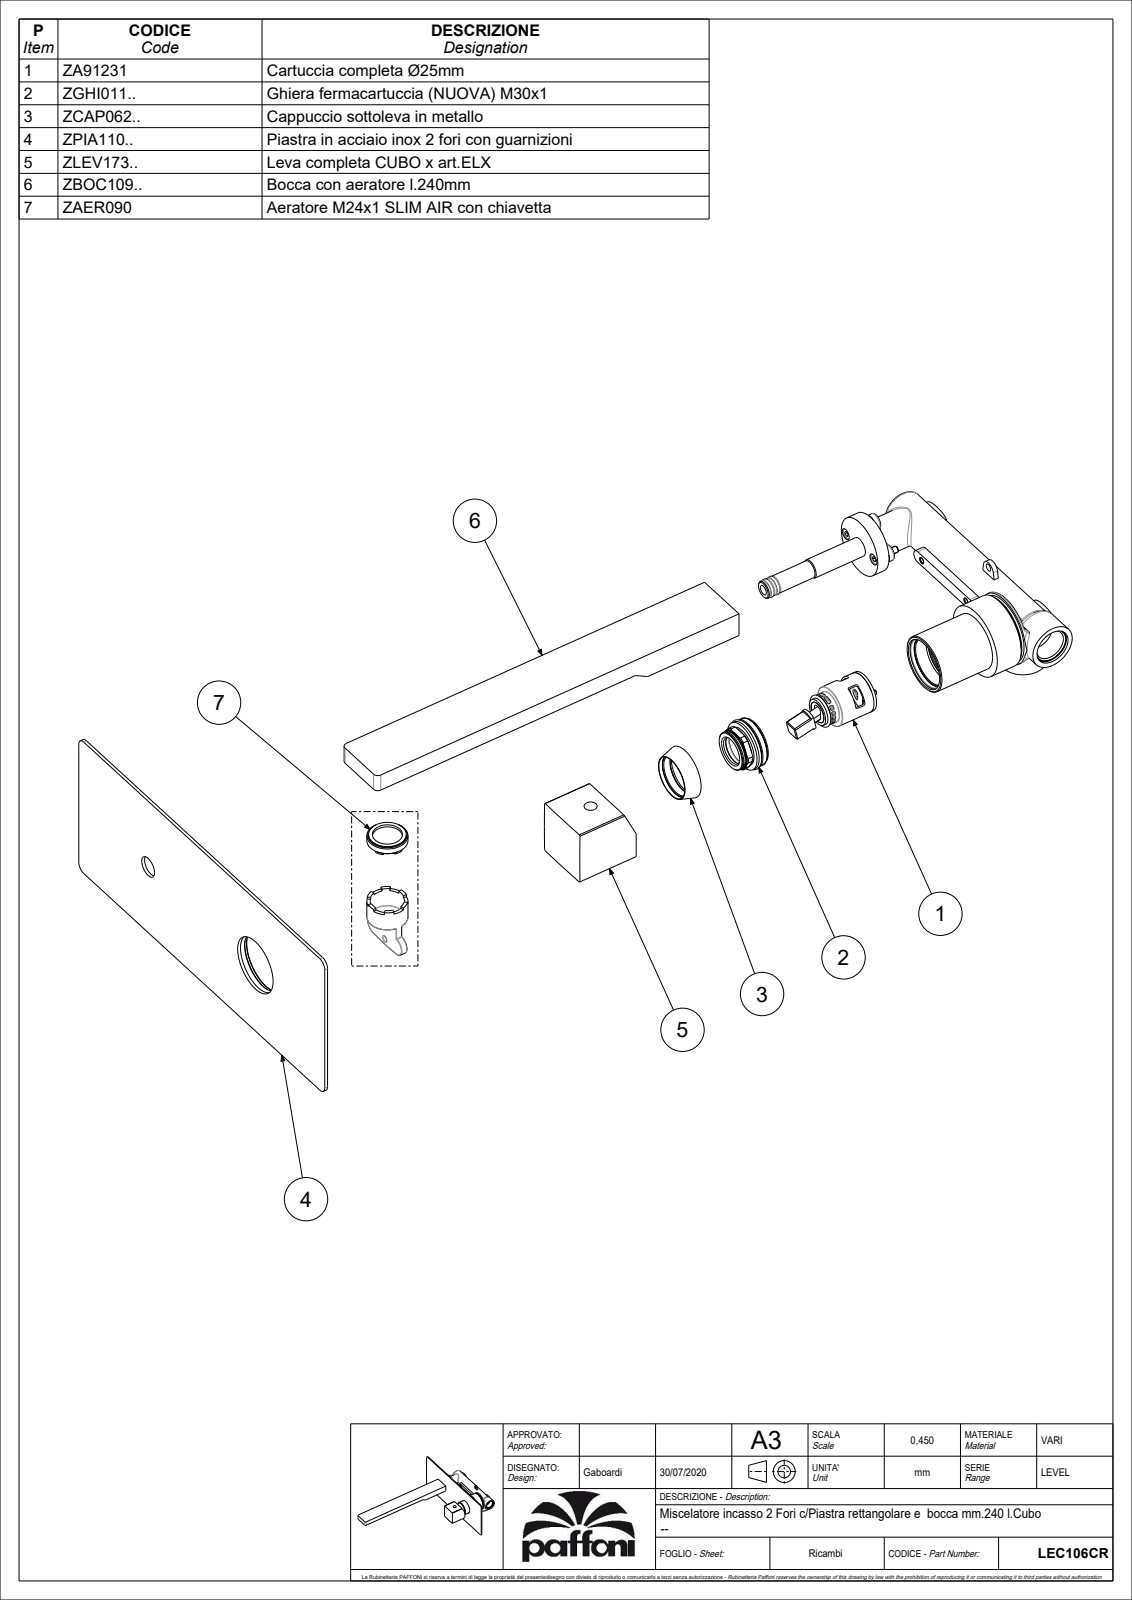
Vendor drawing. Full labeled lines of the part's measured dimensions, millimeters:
Part name (STEP PRODUCT): LEC106CR
STEP written by: CREO PARAMETRIC BY PTC INC, 2020044 (CONFIG_CONTROL_DESIGN)
Units: millimetres
Bodies: 2 solids, 713 faces (233 planar, 261 cylindrical, 219 other)
Overall size (bounding box): 260 × 250 × 100
Volume: 193 399 mm³ · Surface area: 110 237 mm²
Round holes (diameter × count): ⌀6 ×2, ⌀11 ×2, ⌀3 ×1, ⌀4.2 ×1, ⌀5.5 ×1, ⌀12 ×1, ⌀13 ×1, ⌀15 ×1, ⌀16.7 ×1, ⌀17 ×1, ⌀17.5 ×1, ⌀19.2 ×1
Round bosses / shafts (diameter × count): ⌀35.2 ×1, ⌀30 ×1, ⌀27.7 ×1, ⌀25 ×1, ⌀23.8 ×1, ⌀22.5 ×1, ⌀19 ×1, ⌀18.5 ×1
Partial cylindrical surfaces — rounded edges, fillets, slot ends (radius × count): R0.5 ×56, R1 ×7, R2 ×4, R5 ×4, R2.1 ×2, R2.5 ×2, R3 ×2, R3.5 ×2
Main face-to-face distances: 2, 11.5, 35, 9.75, 26.25, 36, 5, 16.5, 14.75, 73.5
Hole centre spacings: 109, 229.94
